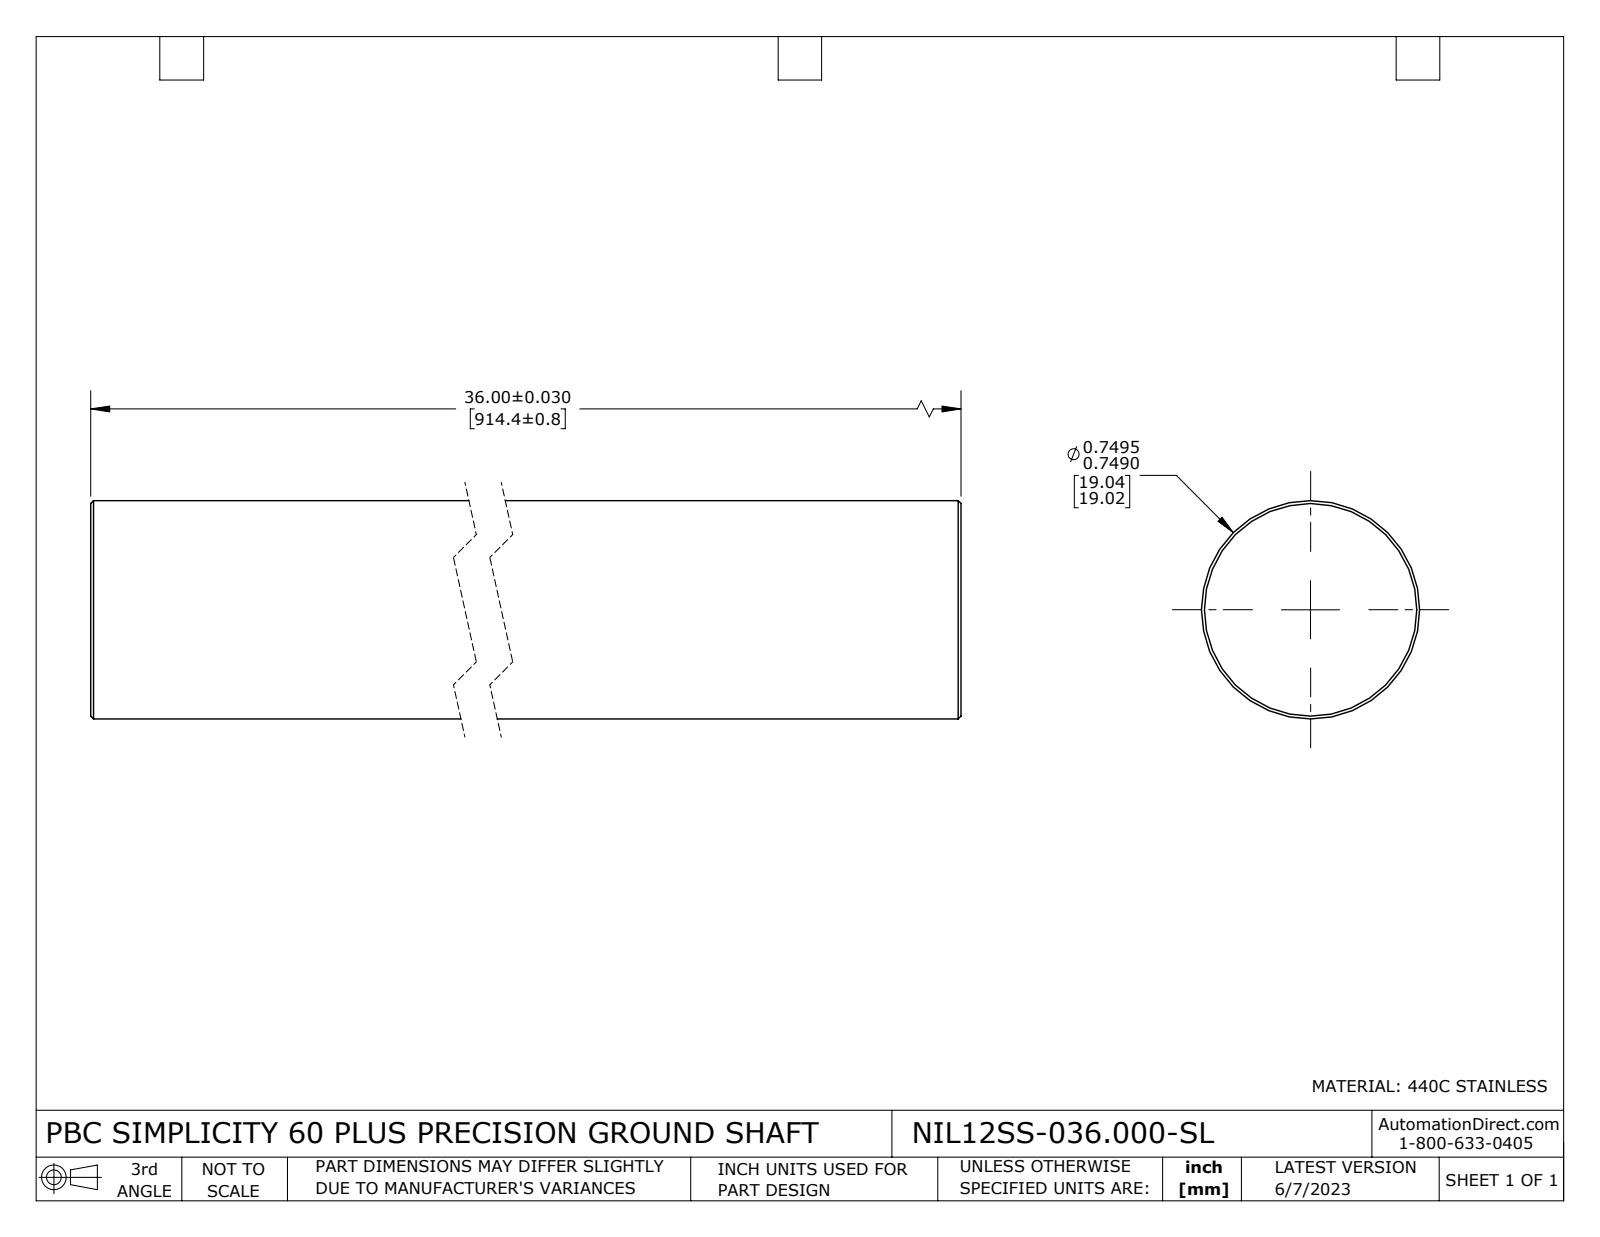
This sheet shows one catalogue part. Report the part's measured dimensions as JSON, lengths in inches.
{"part_name": "NIL12SS-036.000-SL", "step_written_by": "SolidWorks 2021 (CONFIG_CONTROL_DESIGN)", "units": "inches", "bodies": {"solids": 1, "faces": 8, "planar": 2, "cylindrical": 2, "other": 4}, "overall_size": [36, 0.75, 0.75], "volume_in3": 15.9, "surface_area_in2": 85.68, "round_bosses_or_shafts": [[0.75, 1]], "face_to_face_distances": [36]}
